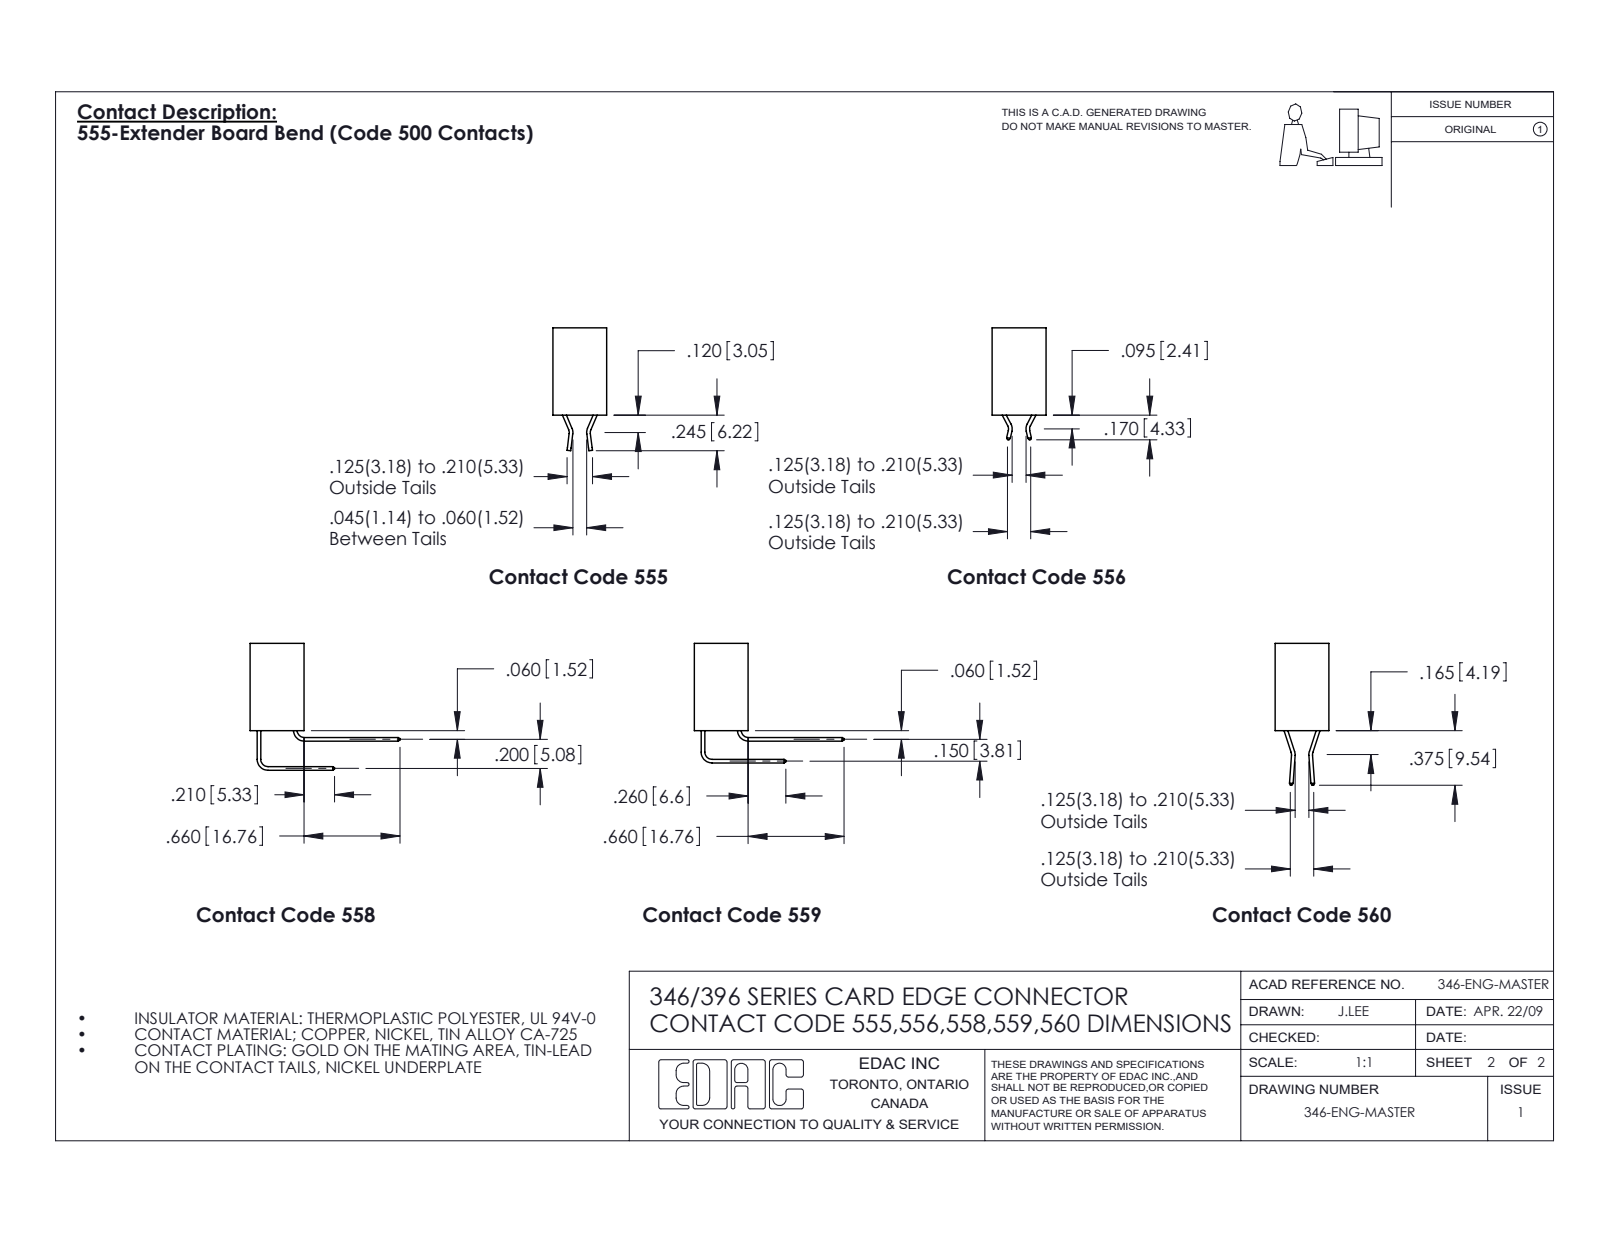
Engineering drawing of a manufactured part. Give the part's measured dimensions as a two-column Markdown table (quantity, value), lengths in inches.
| quantity | value |
| --- | --- |
| part name | 396-094-521-201; 346 Part_No Mounting Lugs; 345-292-001_345-293-121 |
| STEP written by | SolidWorks 2016 (CONFIG_CONTROL_DESIGN) |
| units | inches |
| bodies | 95 solids, 5002 faces (3362 planar, 1640 cylindrical, 0 other) |
| overall size | 6.16 × 0.75 × 0.37 |
| volume | 0.966 in³ |
| surface area | 33.7 in² |
| round holes (diameter × count) | 0.064 × 1 |
| partial cylindrical surfaces (radius × count) | 0.006 × 141, 0.01 × 94, 0.01 × 22, 0.007 × 6, 0.031 × 6, 0.026 × 3, 0.014 × 2, 0.022 × 2 |
| main face-to-face distances | 0.048, 0.322, 0.25, 0.37, 0.072, 0.298, 0.025, 0.275, 0.148, 0.222 |
